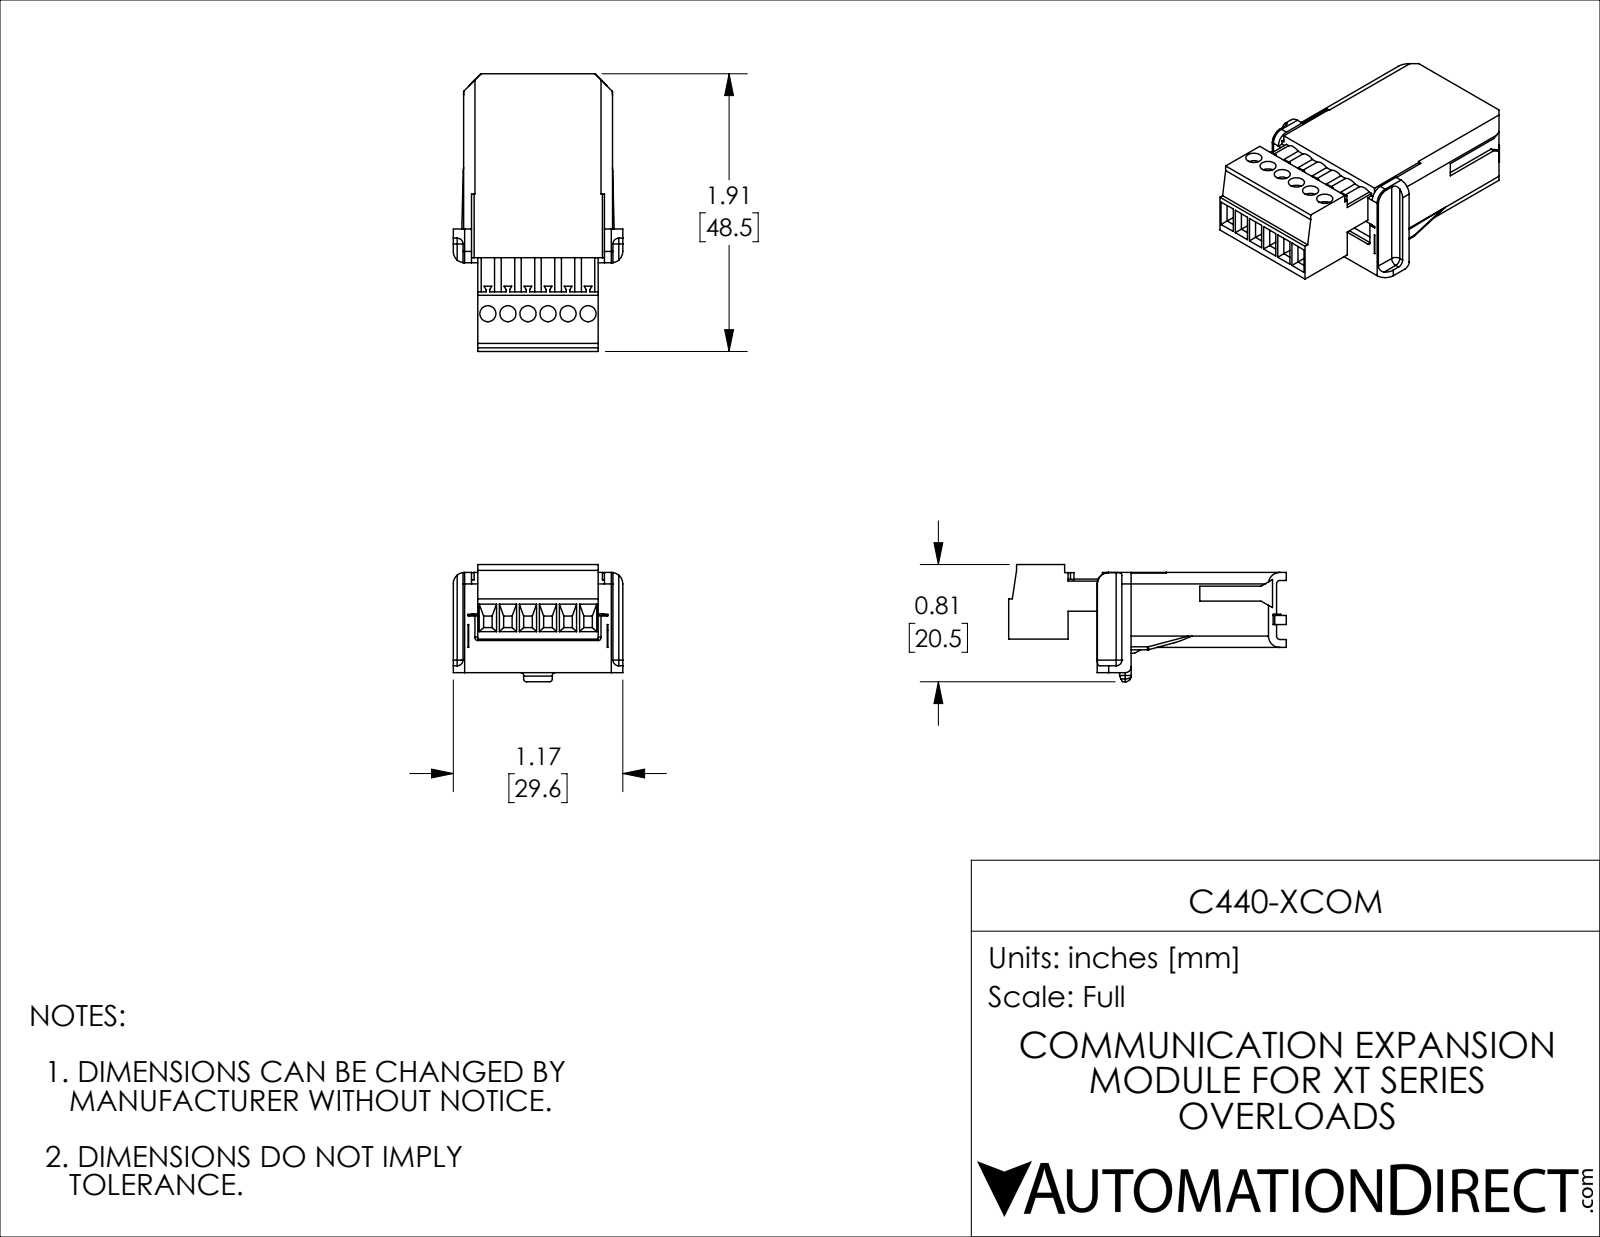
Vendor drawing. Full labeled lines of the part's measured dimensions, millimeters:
Part name (STEP PRODUCT): C440-XCOM
STEP written by: SolidWorks 2018 (AUTOMOTIVE_DESIGN)
Units: millimetres
Bodies: 1 solid, 998 faces (826 planar, 147 cylindrical, 25 other)
Overall size (bounding box): 48.5 × 29.6 × 20.5
Volume: 13 400 mm³ · Surface area: 7 194 mm²
Round holes (diameter × count): ⌀2.8 ×6, ⌀2.4 ×3
Partial cylindrical surfaces — rounded edges, fillets, slot ends (radius × count): R0.1 ×24, R0.5 ×16, R1 ×15, R0.6 ×9, R2 ×9, R2.2 ×6, R2.8 ×6, R0.3 ×4
Main face-to-face distances: 13.1, 1.6, 2.5, 5.6, 23.5, 1.4, 1.4, 2.6, 2.8, 4
Hole centre spacings: 3.5, 7, 10.5, 14, 25.4, 25.7, 26.5, 27.8
